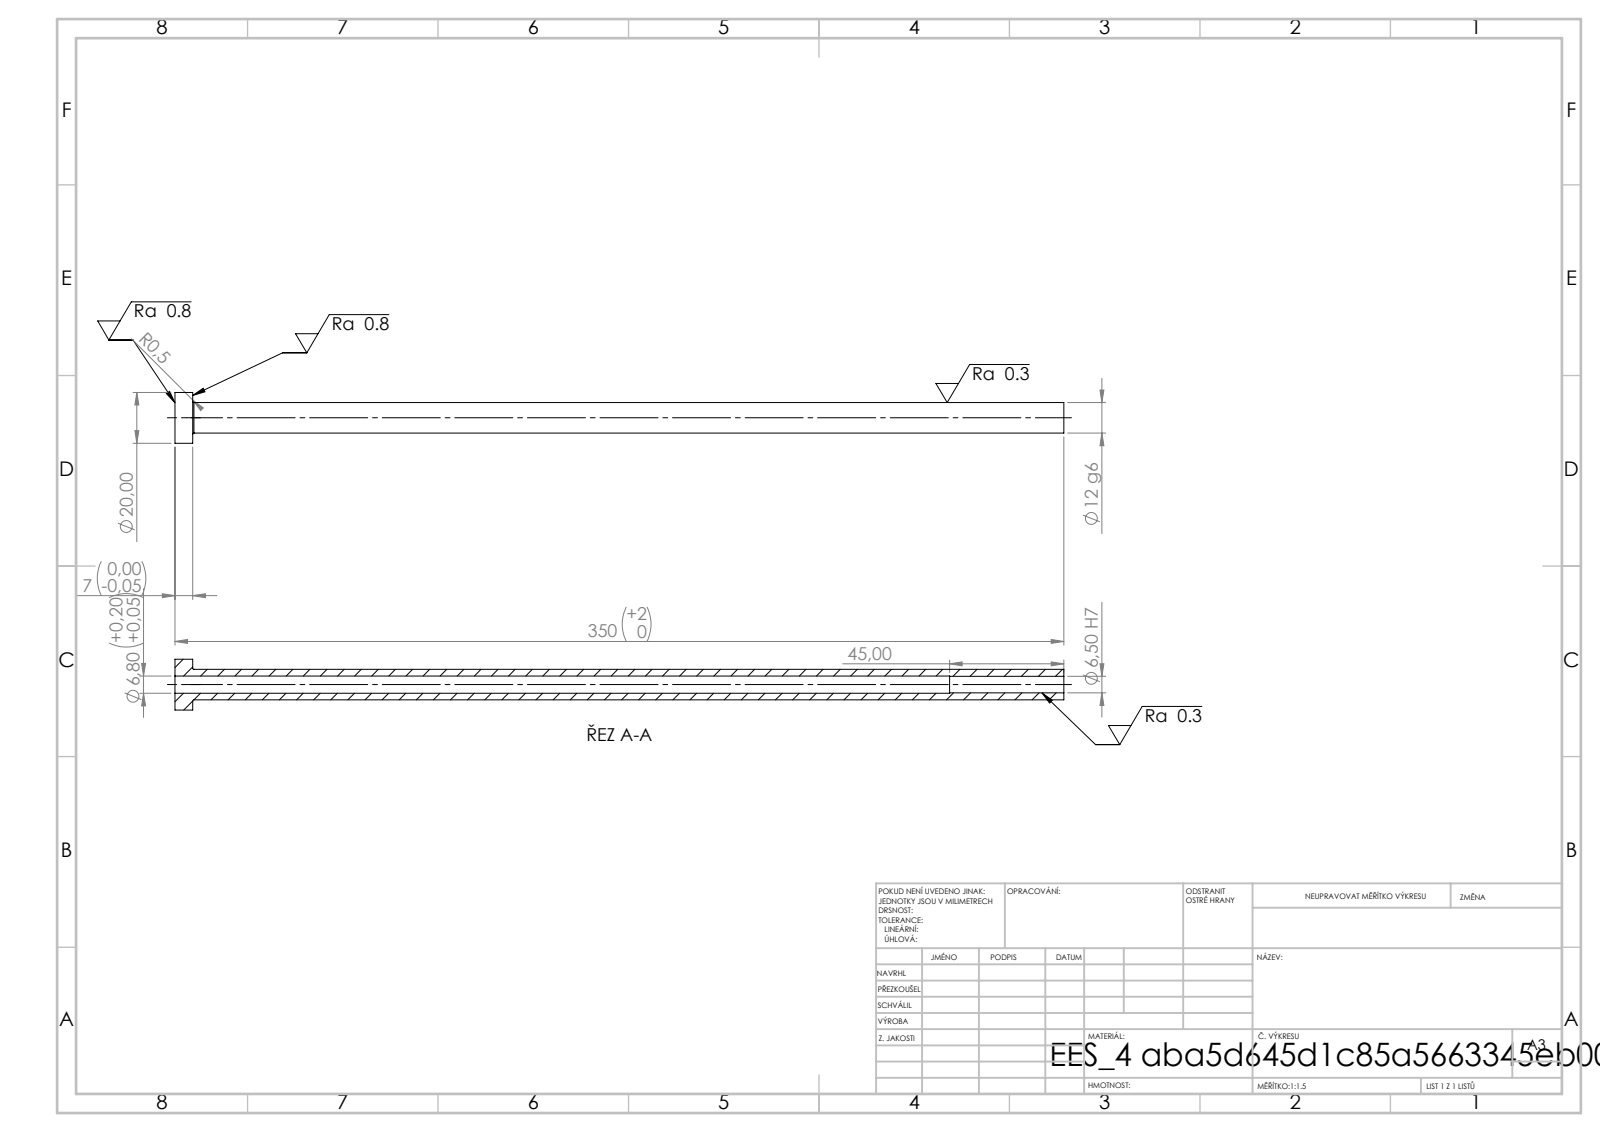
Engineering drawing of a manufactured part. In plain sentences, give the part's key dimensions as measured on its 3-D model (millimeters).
Its 3-D file was written by "SolidWorks 2019 (CONFIG_CONTROL_DESIGN)". It is 1 solid with 14 faces: 4 planar, 8 cylindrical and 2 other. Overall it measures 350 by 20 by 20 millimeters. Its volume is 28 424 cubic millimeters and its surface area 21 359 square millimeters. Round holes: 1 of diameter 6.5, 1 of diameter 6.8. Round bosses or shafts: 1 of diameter 20, 1 of diameter 12. The main face-to-face distances are 7, 350, 343, 305, 298, 45.
